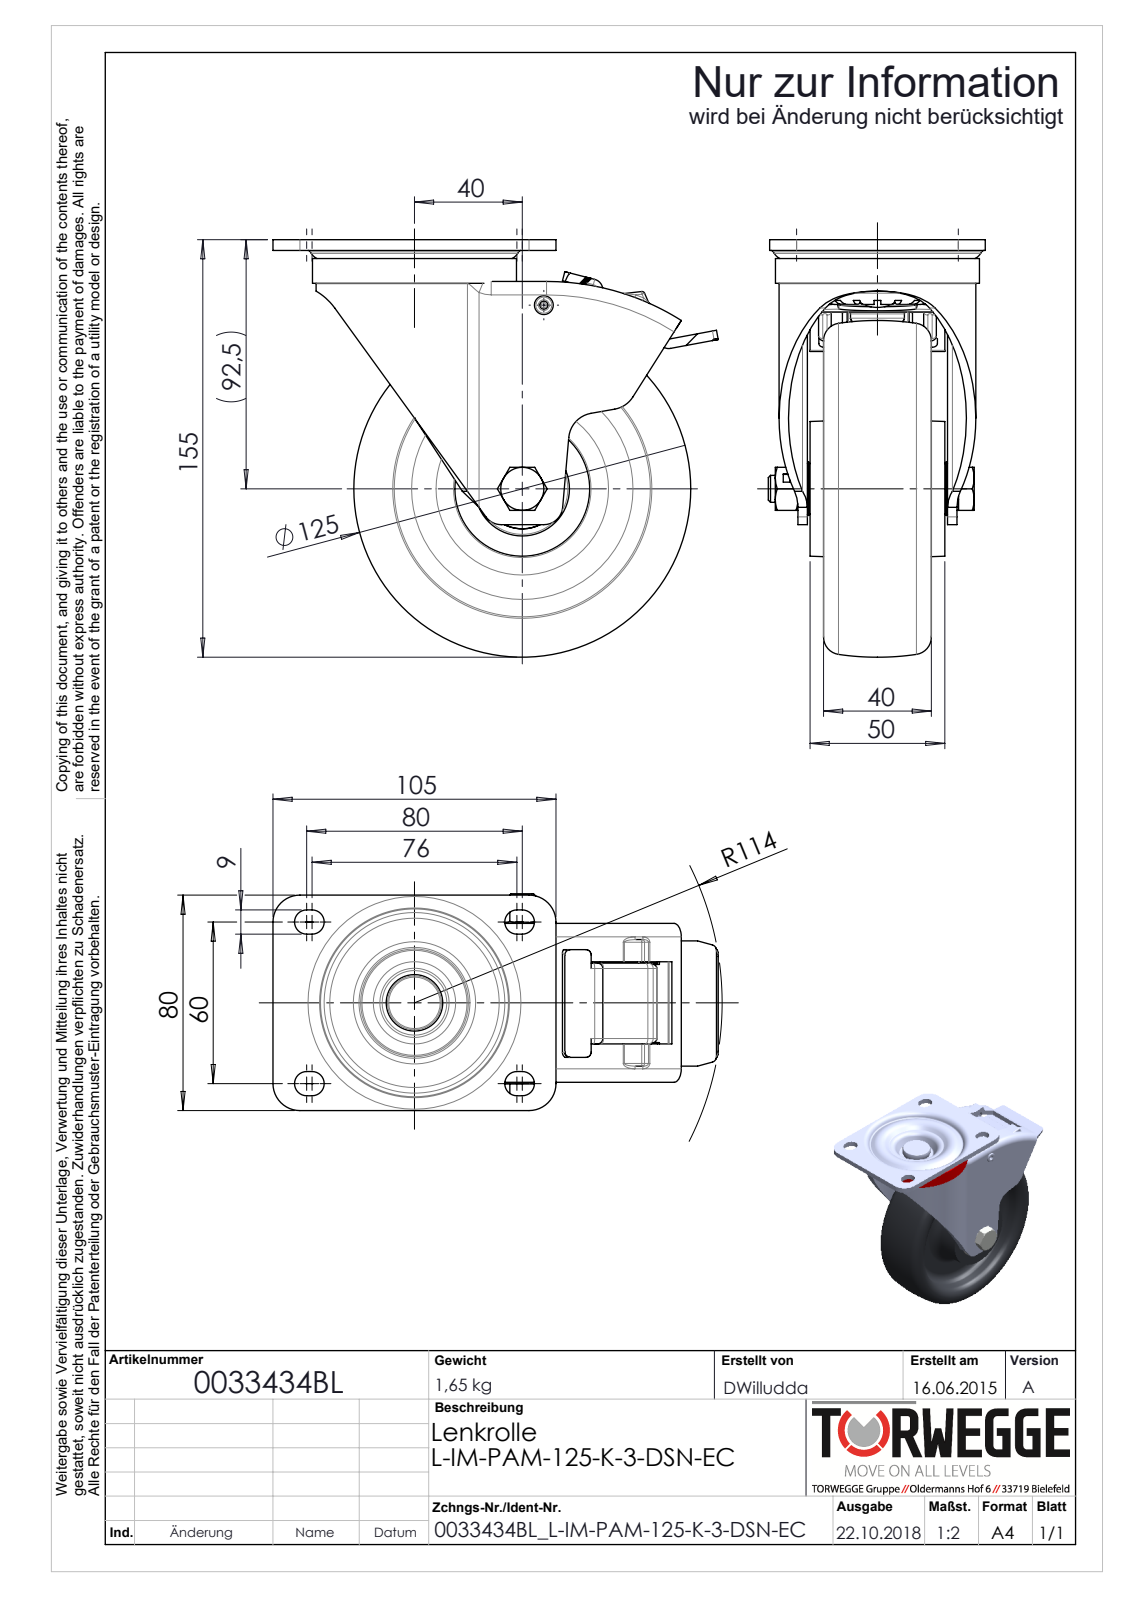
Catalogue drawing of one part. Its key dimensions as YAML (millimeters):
part_name: "0033434BL_L-IM-PAM-125-K-3-DSN-EC"
step_written_by: "SolidWorks 2016 (AUTOMOTIVE_DESIGN)"
units: millimeters
bodies: {solids: 25, faces: 1223, planar: 588, cylindrical: 314, other: 321}
overall_size: [165.19, 155, 80.5]
volume: 474948
surface_area: 174387
round_holes:
  - {diameter: 3, count: 1}
  - {diameter: 5, count: 1}
  - {diameter: 5.2, count: 1}
  - {diameter: 8.5, count: 1}
  - {diameter: 10, count: 1}
  - {diameter: 10.35, count: 1}
  - {diameter: 10.5, count: 1}
  - {diameter: 12.5, count: 1}
  - {diameter: 15, count: 1}
  - {diameter: 16, count: 1}
  - {diameter: 20.3, count: 1}
  - {diameter: 28.48, count: 1}
round_bosses_or_shafts:
  - {diameter: 75.69, count: 1}
  - {diameter: 35, count: 1}
  - {diameter: 21.52, count: 1}
  - {diameter: 21, count: 1}
  - {diameter: 20, count: 1}
  - {diameter: 19.75, count: 1}
  - {diameter: 14.9, count: 1}
  - {diameter: 12.5, count: 1}
partial_cylinders:
  - {radius: 2, count: 22}
  - {radius: 0.5, count: 12}
  - {radius: 4.5, count: 9}
  - {radius: 0.27, count: 8}
  - {radius: 1.5, count: 8}
  - {radius: 10, count: 8}
  - {radius: 0.15, count: 7}
  - {radius: 0.45, count: 7}
face_to_face_distances: [3.5, 55.5, 1, 4, 24.5, 34.5, 21, 31, 59, 52]
hole_center_spacings: [68.67]
